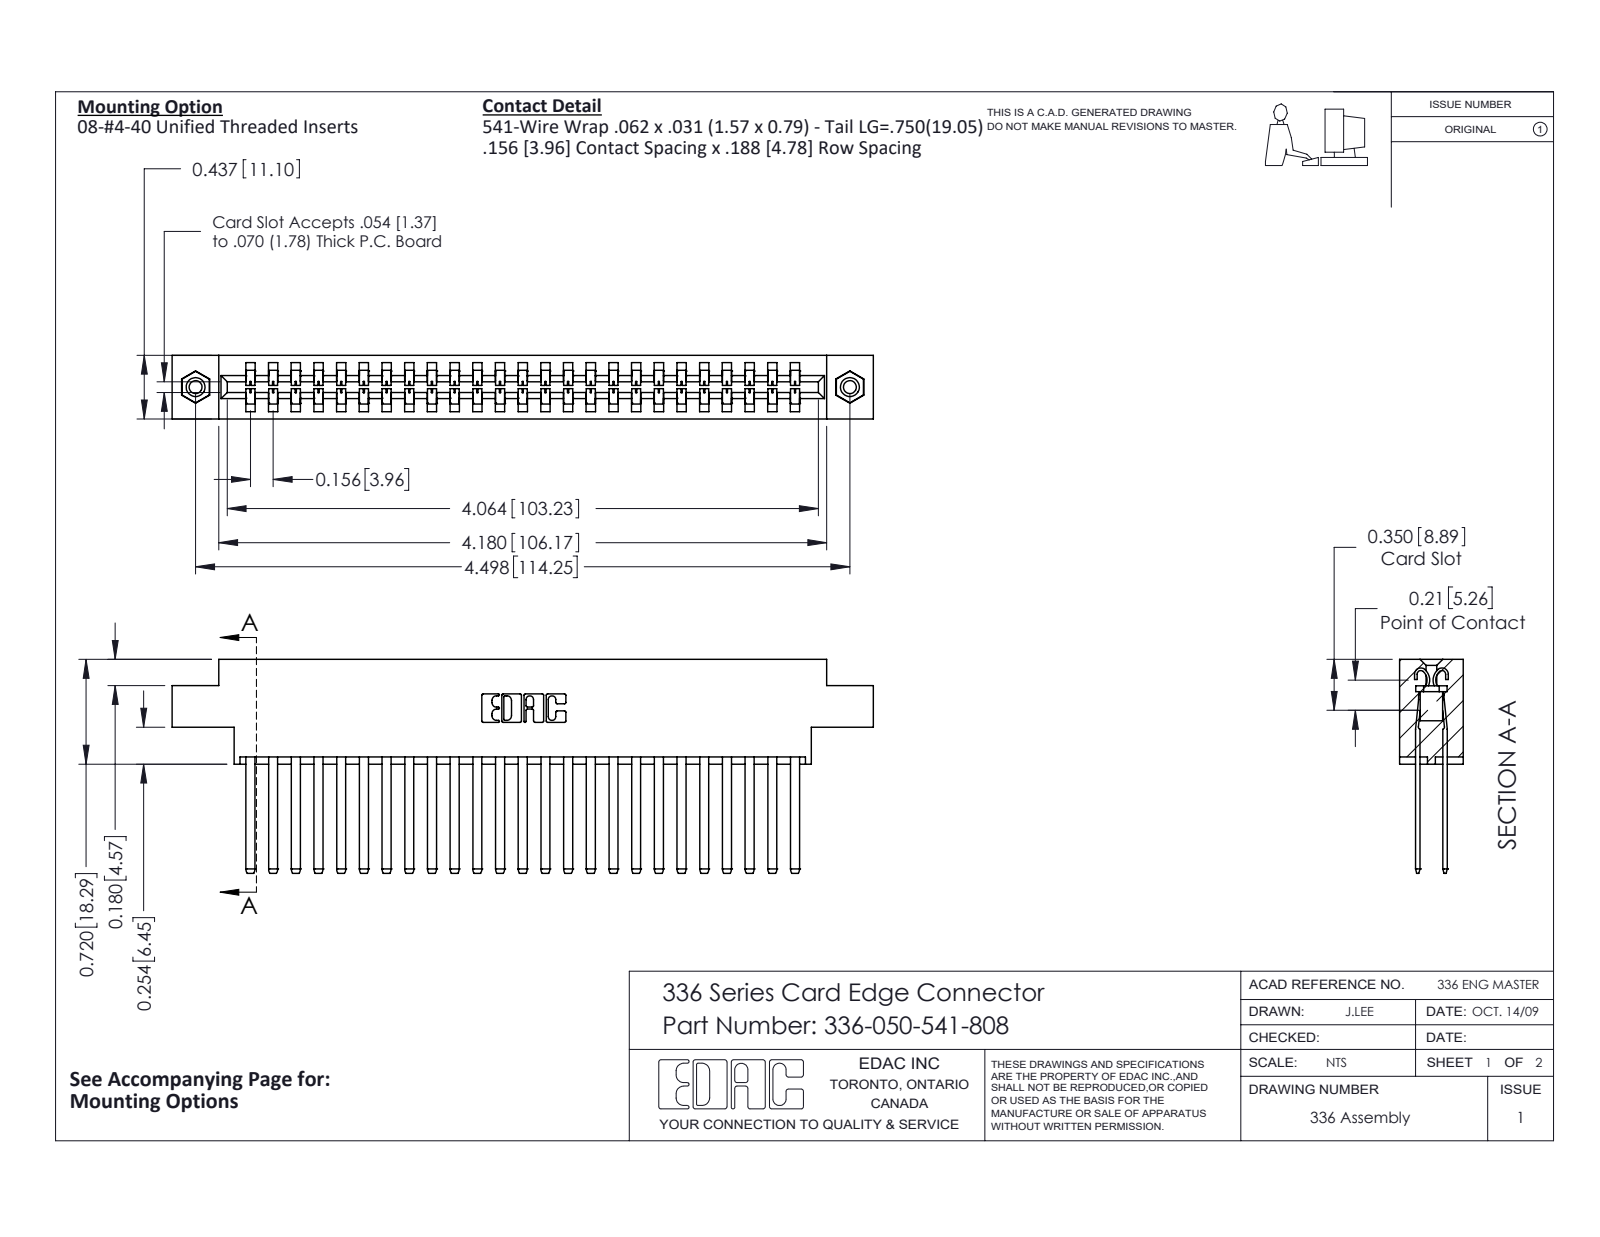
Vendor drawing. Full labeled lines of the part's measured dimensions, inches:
Part name (STEP PRODUCT): 336 Part_Offset - .156 Dia - TI; 336-290-001_336-290-541; 345-250-001_345-250-003-102; 336-050-541-808
STEP written by: SolidWorks 2020 (CONFIG_CONTROL_DESIGN)
Units: inches
Bodies: 53 solids, 2278 faces (1406 planar, 856 cylindrical, 16 other)
Overall size (bounding box): 4.821 × 1.47 × 0.437
Volume: 1.12 in³ · Surface area: 36.03 in²
Round holes (diameter × count): ⌀0.089 ×2, ⌀0.125 ×2, ⌀0.156 ×2
Round bosses / shafts (diameter × count): ⌀0.155 ×2
Partial cylindrical surfaces — rounded edges, fillets, slot ends (radius × count): R0.004 ×100, R0.056 ×50, R0.01 ×22, R0.007 ×6, R0.031 ×6, R0.022 ×4, R0.04 ×4, R0.026 ×3
Main face-to-face distances: 0.188, 0.328, 0.14, 0.297, 0.109, 0.031, 0.437, 0.033, 0.181, 0.146
Hole centre spacings: 4.498
